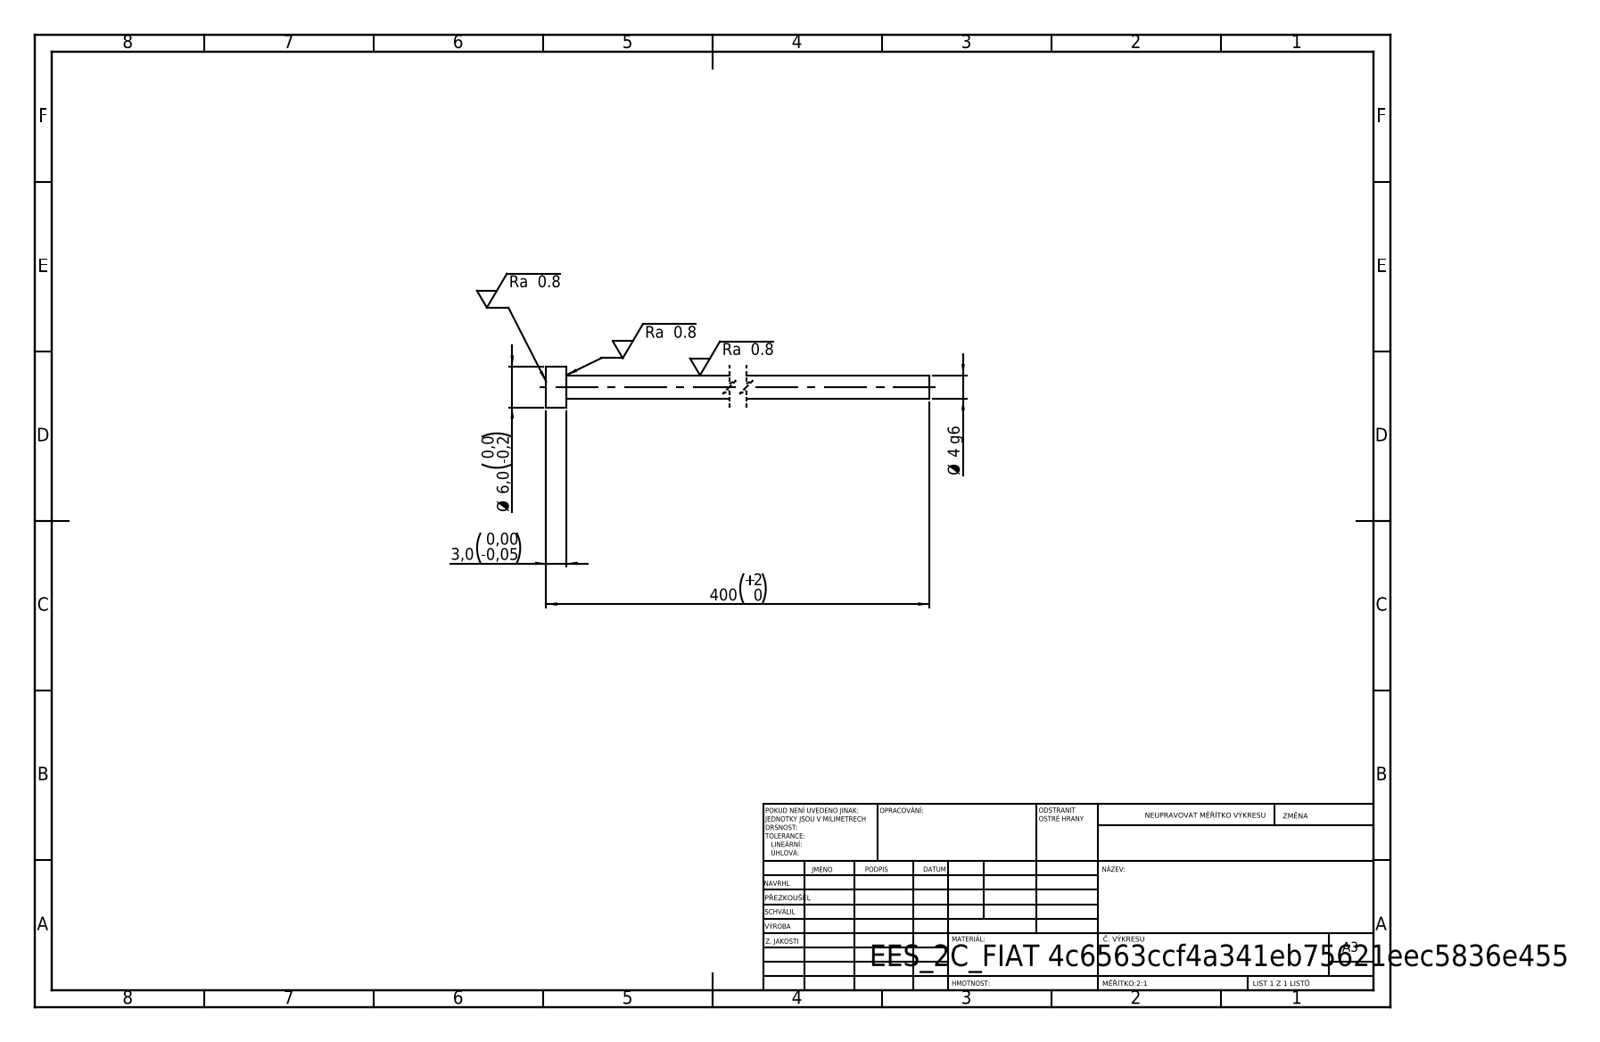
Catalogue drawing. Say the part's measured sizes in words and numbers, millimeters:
Its 3-D file was written by "SolidWorks 2019 (CONFIG_CONTROL_DESIGN)". It is 1 solid with 7 faces: 3 planar, 4 cylindrical and 0 other. Overall it measures 400 by 6 by 6 millimeters. Its volume is 3 904 cubic millimeters and its surface area 4 478 square millimeters. Round bosses or shafts: 1 of diameter 6, 1 of diameter 3.5. The main face-to-face distances are 3, 400, 397.
